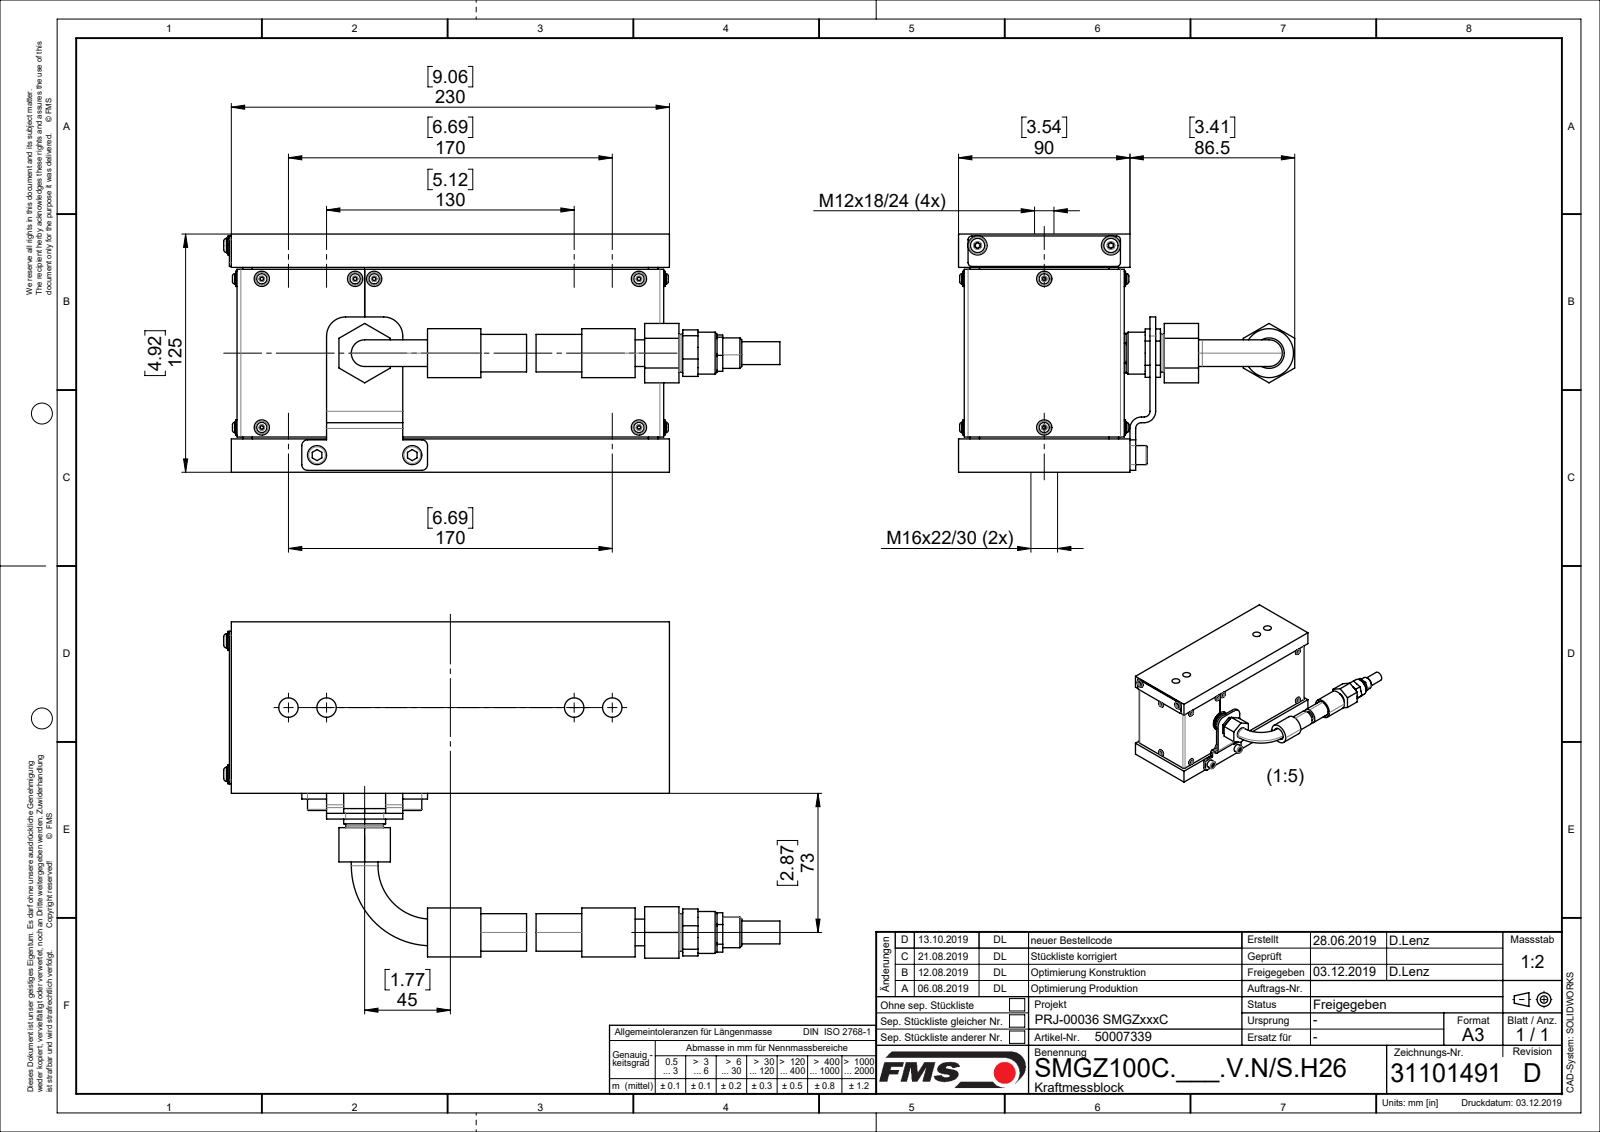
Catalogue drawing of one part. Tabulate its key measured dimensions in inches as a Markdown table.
| quantity | value |
| --- | --- |
| part name | 31101498_01; 31101497_01; 31101461_stp_01; 31101516_01 (+8 more) |
| STEP written by | SolidWorks 2018 (CONFIG_CONTROL_DESIGN) |
| units | inches |
| bodies | 49 solids, 1509 faces (370 planar, 911 cylindrical, 228 other) |
| overall size | 11.496 × 6.949 × 4.921 |
| volume | 147.6 in³ |
| surface area | 667.2 in² |
| round holes (diameter × count) | 0.157 × 17, 0.098 × 14, 0.213 × 14, 0.402 × 4, 0.551 × 4, 0.394 × 3, 0.13 × 2, 0.165 × 2, 0.197 × 2, 0.256 × 2, 0.295 × 2, 0.354 × 2 |
| round bosses / shafts (diameter × count) | 0.315 × 14, 0.118 × 14, 0.394 × 4, 0.866 × 2, 0.776 × 2, 0.669 × 2, 0.61 × 2, 0.236 × 2 |
| partial cylindrical surfaces (radius × count) | 0.011 × 216, 0.016 × 24, 0.039 × 20, 0.079 × 16, 0.118 × 6, 0.236 × 2, 0.394 × 2 |
| main face-to-face distances | 0.039, 0.079, 0.118, 3.189, 3.15, 3.228, 3.11, 3.268, 3.071, 3.307 |
| hole center spacings | 3.071, 0.394, 1.548, 1.929, 2.2, 2.323, 2.496, 3.096 |
